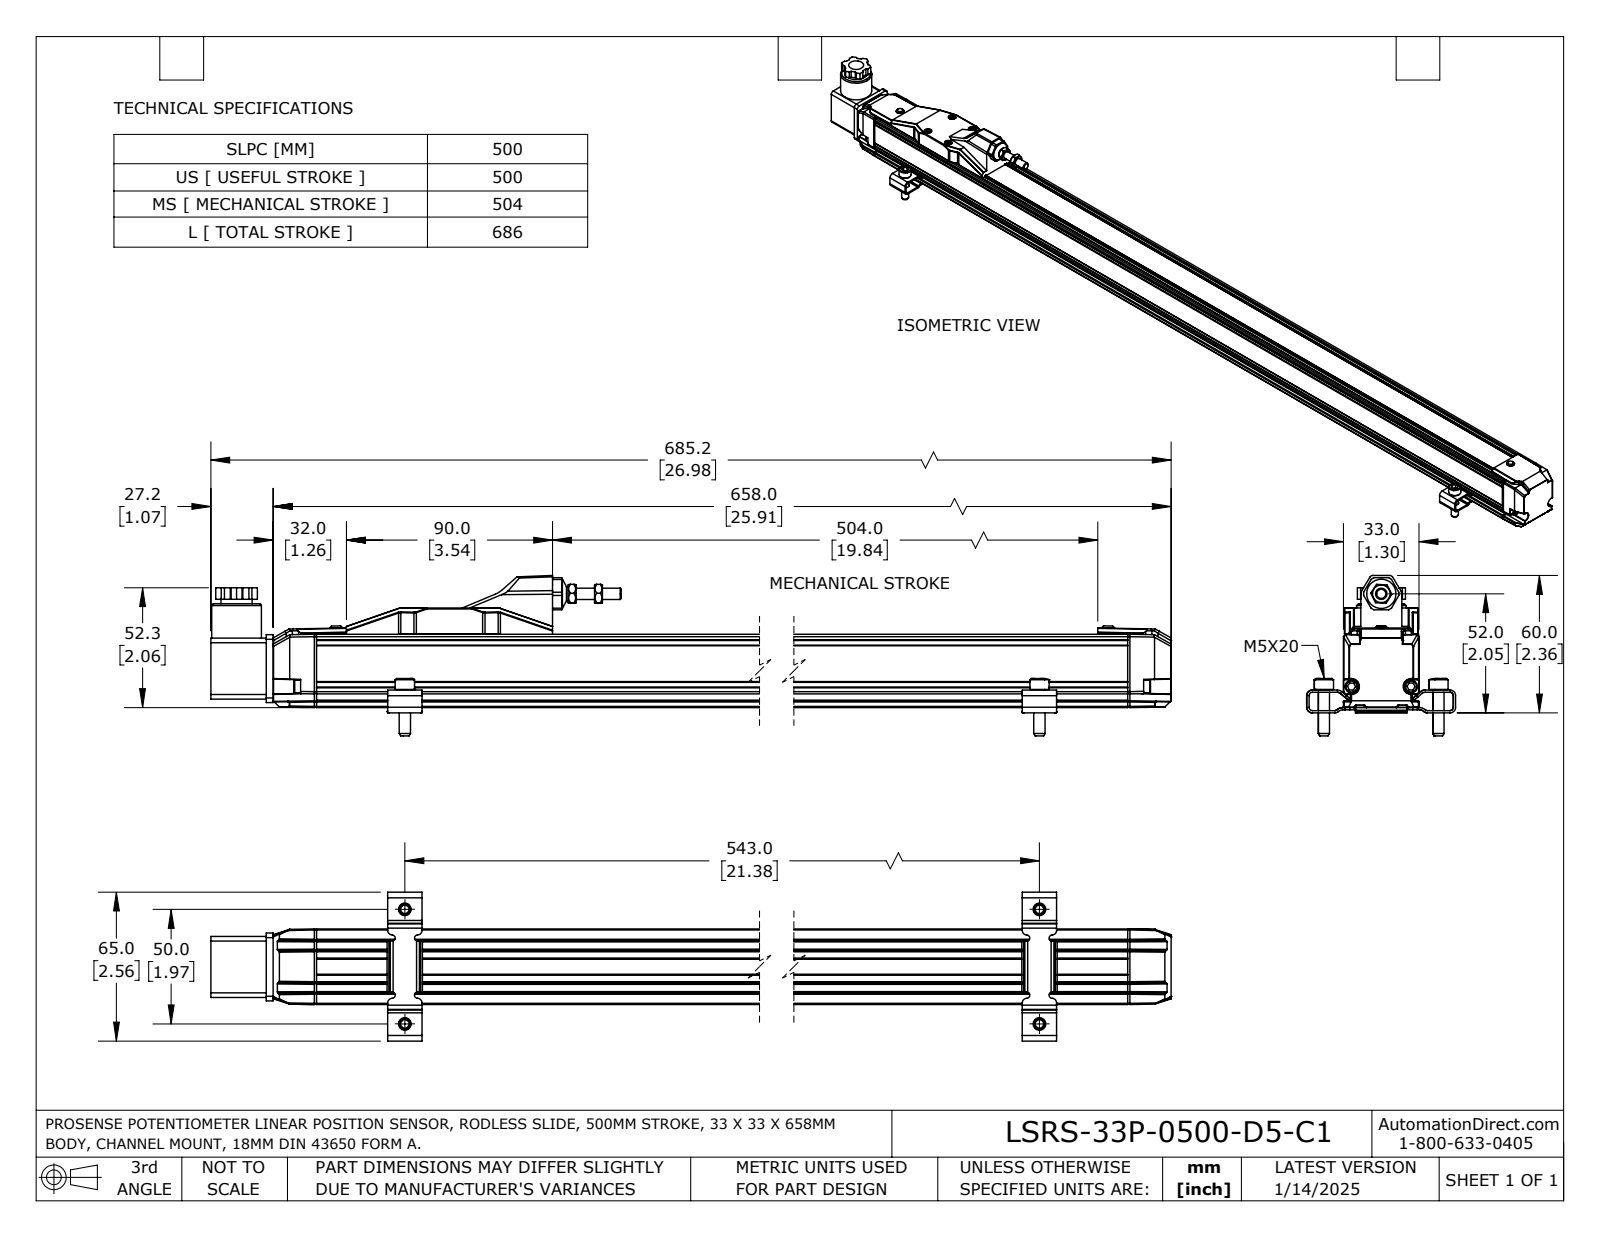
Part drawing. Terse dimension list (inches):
name: LSRS-33P-0500-D5-C1
written by: SolidWorks 2023 (AUTOMOTIVE_DESIGN)
unit: in
bodies: 11 solids, 1336 faces (841 planar, 363 cylindrical, 132 other)
size: 26.976 × 2.754 × 2.559
volume: 40.15 in³; area: 253.5 in²
holes: 4× ⌀0.185, 4× ⌀0.217, 2× ⌀0.106, 2× ⌀0.13, 1× ⌀0.11, 1× ⌀0.157, 1× ⌀0.197, 1× ⌀0.209, 1× ⌀0.232, 1× ⌀0.236, 1× ⌀0.276, 1× ⌀0.394
bosses: 4× ⌀0.331, 4× ⌀0.193, 4× ⌀0.181, 4× ⌀0.113, 2× ⌀0.22, 2× ⌀0.217, 2× ⌀0.118, 2× ⌀0.098
rounds: 82× R0.02, 62× R0.008, 44× R0.079, 26× R0.118, 10× R0.039, 8× R0.051, 8× R0.059, 8× R0.157
face distances: 1.299, 0.118, 1.244, 1.167, 0.237, 1.007, 0.035, 0.014, 1.285, 0.443
hole spacings: 0.597, 0.787, 0.933, 1.221, 1.286, 1.673, 1.969, 20.223
